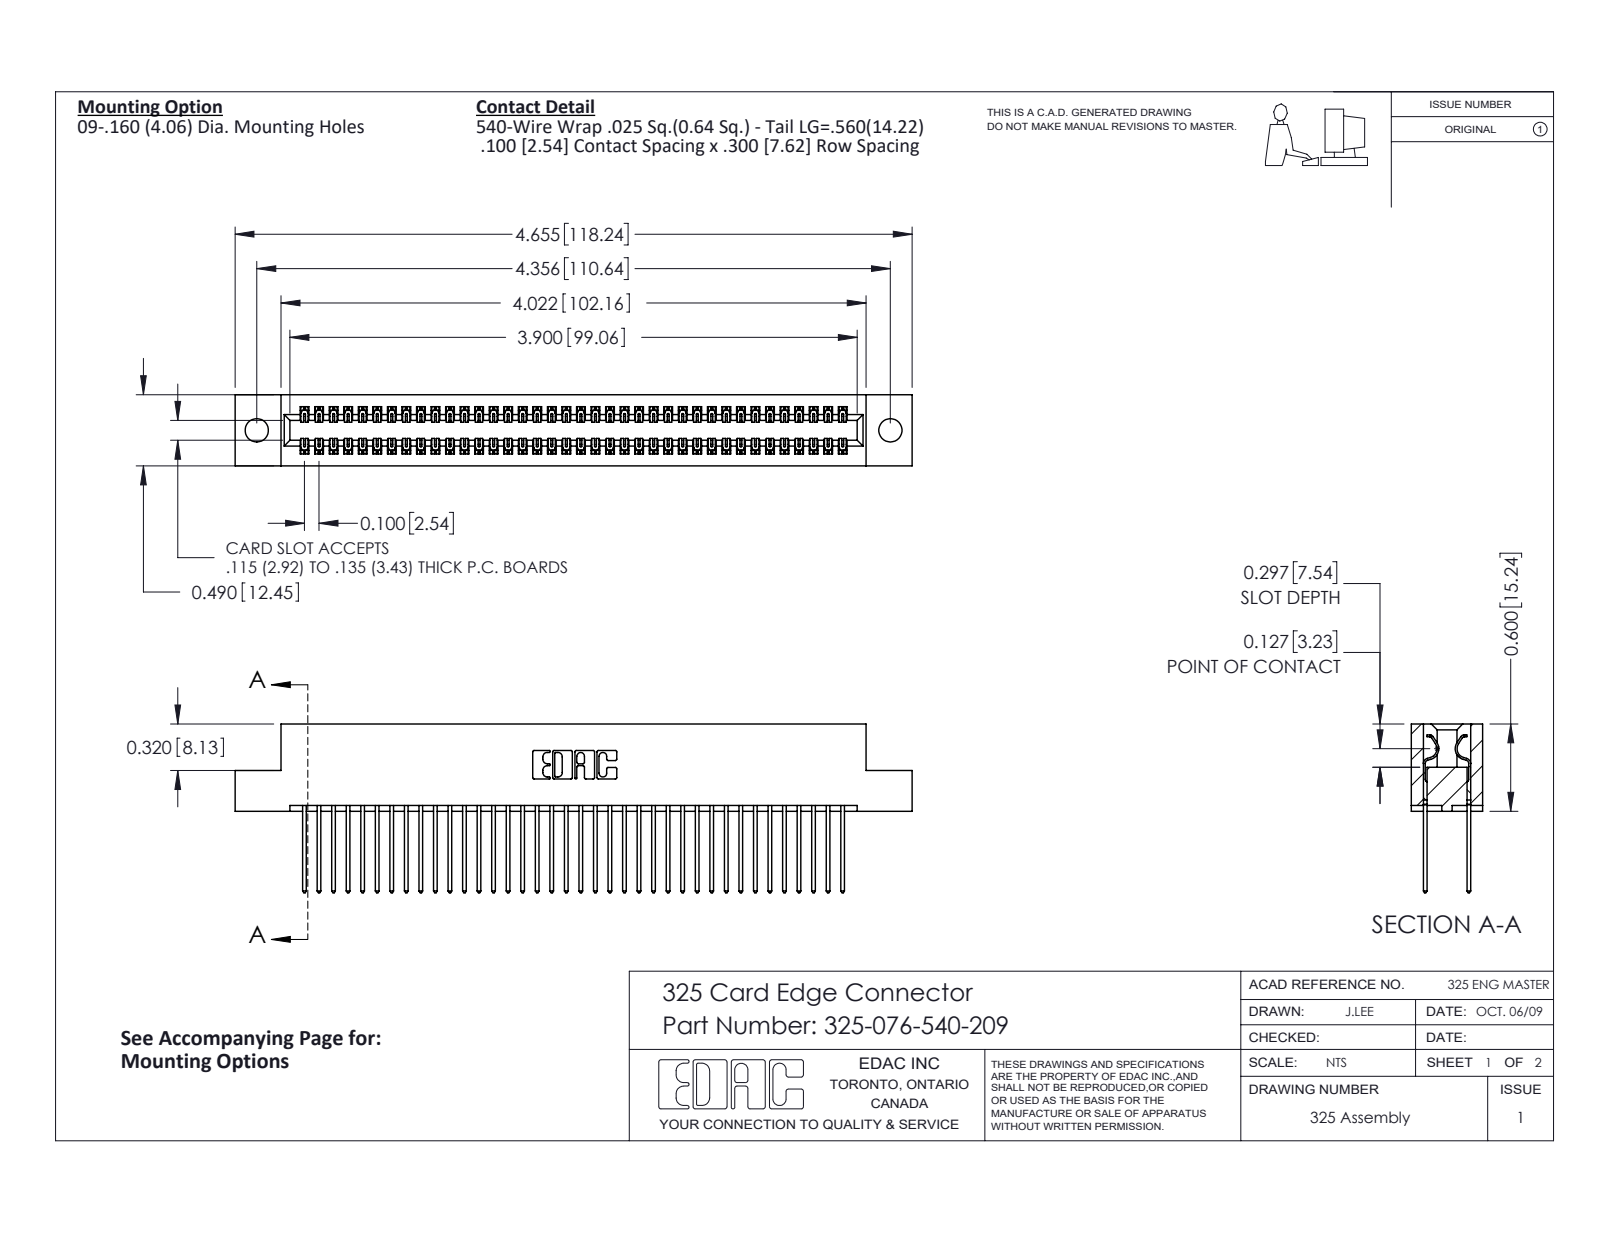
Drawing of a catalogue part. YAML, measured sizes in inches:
part_name: "325-076-540-209; 325 Part_.160 TH; 325-292-001_325-293-140"
step_written_by: "SolidWorks 2016 (CONFIG_CONTROL_DESIGN)"
units: inches
bodies: {solids: 77, faces: 4066, planar: 2806, cylindrical: 1260, other: 0}
overall_size: [4.655, 1.16, 0.49]
volume: 0.933
surface_area: 30.53
round_holes:
  - {diameter: 0.16, count: 2}
partial_cylinders:
  - {radius: 0.006, count: 114}
  - {radius: 0.01, count: 76}
  - {radius: 0.01, count: 22}
  - {radius: 0.007, count: 6}
  - {radius: 0.031, count: 6}
  - {radius: 0.026, count: 3}
  - {radius: 0.014, count: 2}
  - {radius: 0.022, count: 2}
face_to_face_distances: [0.083, 0.407, 0.3, 0.107, 0.383, 0.025, 0.49, 0.325, 0.275, 0.56]
hole_center_spacings: [4.356]
